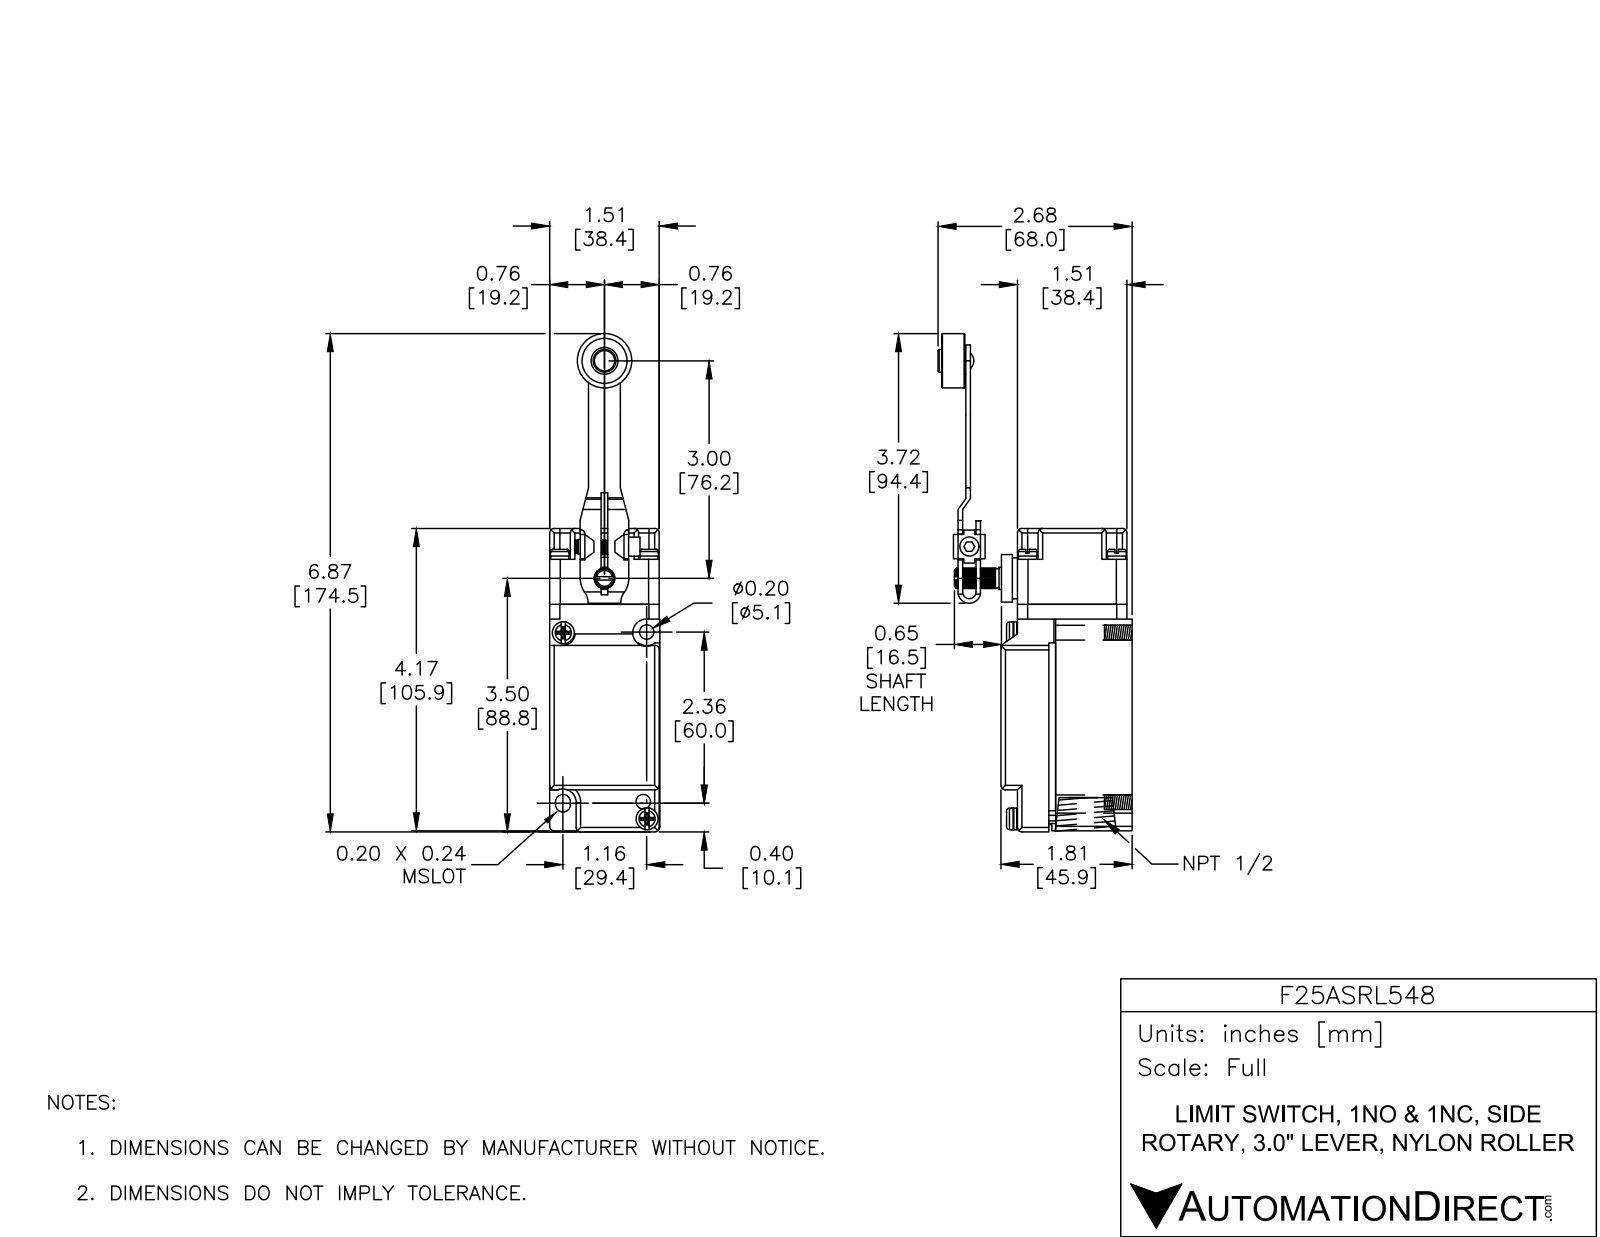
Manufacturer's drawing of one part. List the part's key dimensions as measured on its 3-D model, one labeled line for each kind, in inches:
Part name (STEP PRODUCT): F25ASRL548; Imported150; Imported153; Imported152 (+8 more)
STEP written by: SolidWorks 2002296 (CONFIG_CONTROL_DESIGN)
Units: inches
Bodies: 17 solids, 931 faces (513 planar, 235 cylindrical, 183 other)
Overall size (bounding box): 6.872 × 2.678 × 1.52
Volume: 10.39 in³ · Surface area: 75.32 in²
Round holes (diameter × count): ⌀0.177 ×4, ⌀0.19 ×3, ⌀0.2 ×3, ⌀0.156 ×1, ⌀0.17 ×1, ⌀0.251 ×1, ⌀0.58 ×1, ⌀0.62 ×1
Round bosses / shafts (diameter × count): ⌀0.26 ×4, ⌀0.25 ×4, ⌀0.302 ×2, ⌀0.3 ×2, ⌀0.75 ×1, ⌀0.655 ×1, ⌀0.565 ×1, ⌀0.375 ×1
Partial cylindrical surfaces — rounded edges, fillets, slot ends (radius × count): R0.062 ×29, R0.03 ×16, R0.015 ×8, R0.145 ×8, R0.063 ×4, R0.14 ×4, R0.032 ×3, R0.025 ×2
Main face-to-face distances: 0.094, 1.149, 1.055, 1.52, 0.66, 0.754, 1.809, 1.51, 0.433, 0.063
Hole centre spacings: 1.23, 1.23, 1.74, 2.815, 0.225, 0.235, 0.936, 0.942
